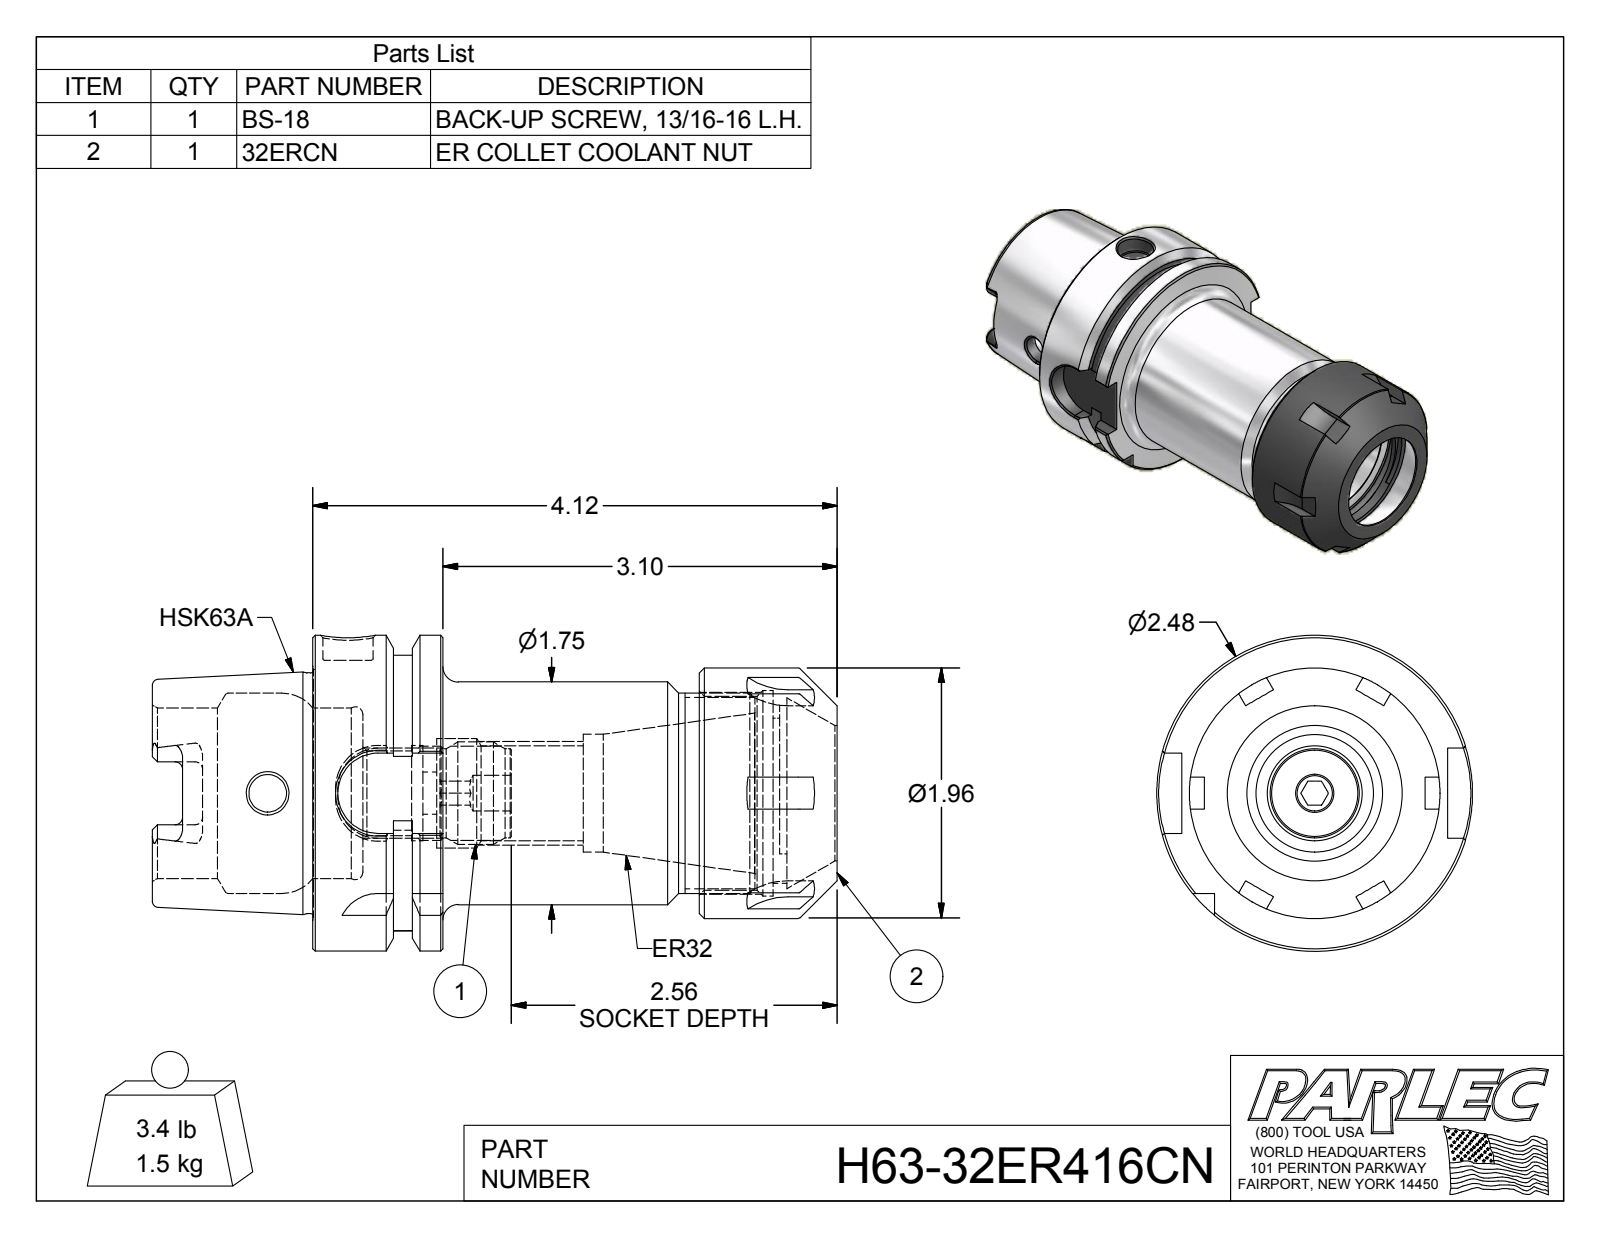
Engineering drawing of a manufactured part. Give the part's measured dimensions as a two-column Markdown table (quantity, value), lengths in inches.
| quantity | value |
| --- | --- |
| part name | H63-32ER416CN; H63-32ER4-1; 32ERCN; BS-18 |
| STEP written by | Autodesk Inventor 2012 (AUTOMOTIVE_DESIGN) |
| units | inches |
| bodies | 3 solids, 205 faces (84 planar, 53 cylindrical, 68 other) |
| overall size | 5.38 × 2.48 × 2.48 |
| volume | 10.26 in³ |
| surface area | 72.26 in² |
| round holes (diameter × count) | 0.28 × 1, 0.295 × 1, 0.331 × 1, 0.394 × 1, 0.666 × 1, 0.745 × 1, 0.749 × 1, 0.861 × 1, 0.925 × 1, 1.063 × 1, 1.299 × 1, 1.339 × 1 |
| round bosses / shafts (diameter × count) | 2.48 × 1, 1.969 × 1, 1.891 × 1, 1.75 × 1, 0.805 × 1, 0.7 × 1 |
| partial cylindrical surfaces (radius × count) | 0.059 × 6, 0.5 × 6, 0.113 × 4, 0.315 × 4, 0.689 × 1, 1.083 × 1 |
| main face-to-face distances | 1.024, 0.241, 0.389, 0.394, 0.63, 3.037, 2.644, 2.014, 3.616, 3.222 |
| hole center spacings | 0.059 |
